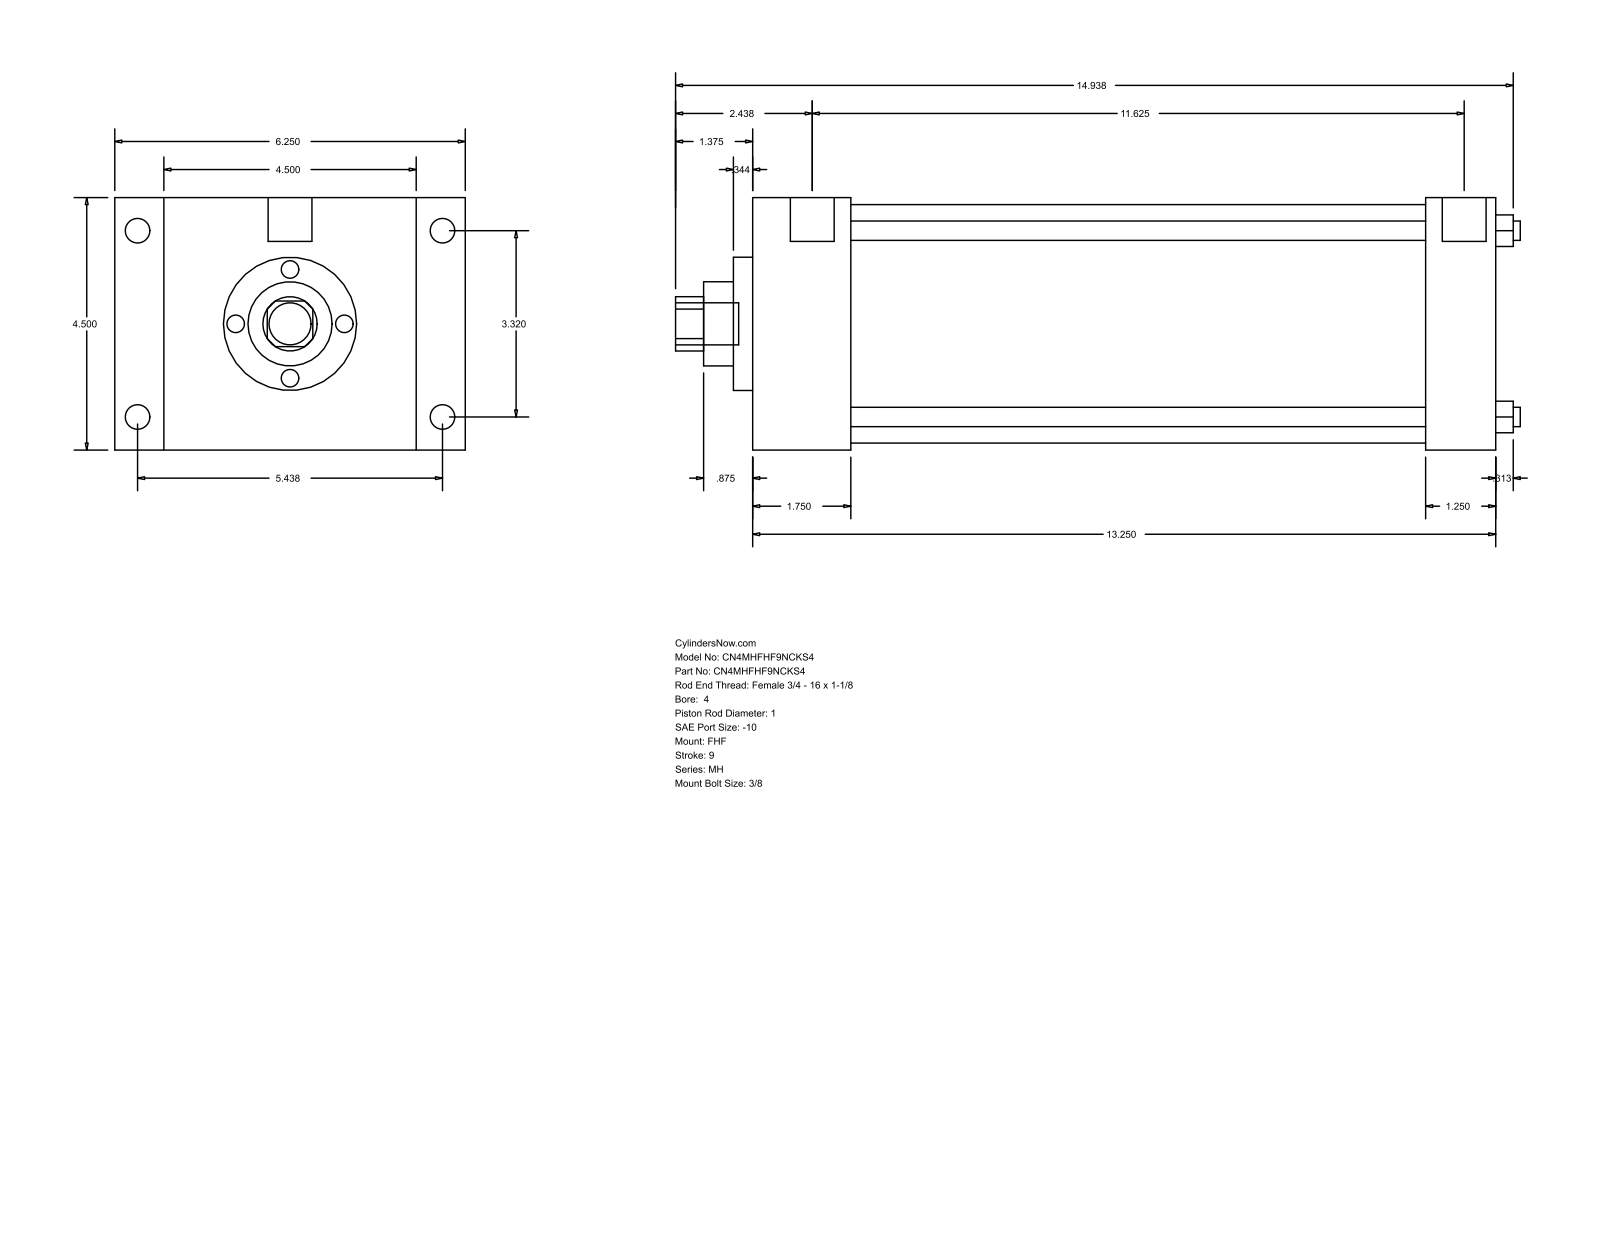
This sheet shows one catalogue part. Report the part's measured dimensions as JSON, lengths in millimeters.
{"part_name": "MH_FHF__0400_1", "step_written_by": "GSSL Pune (CONFIG_CONTROL_DESIGN)", "units": "millimeters", "bodies": {"solids": 0, "faces": 90, "planar": 61, "cylindrical": 29, "other": 0}, "overall_size": [382.59, 158.75, 114.3], "round_holes": [[8.76, 4], [25.4, 1], [38.1, 1], [60.33, 1], [107.95, 1]], "round_bosses_or_shafts": [[11.13, 4], [8.73, 4], [19.84, 2], [19.05, 1]], "partial_cylinders_radius": [[12.29, 1]], "face_to_face_distances": [114.3, 336.56, 44.46, 292.1, 22.23, 136.53, 158.76, 304.81, 260.35, 31.75], "hole_center_spacings": [59.62, 84.32, 119.25]}
